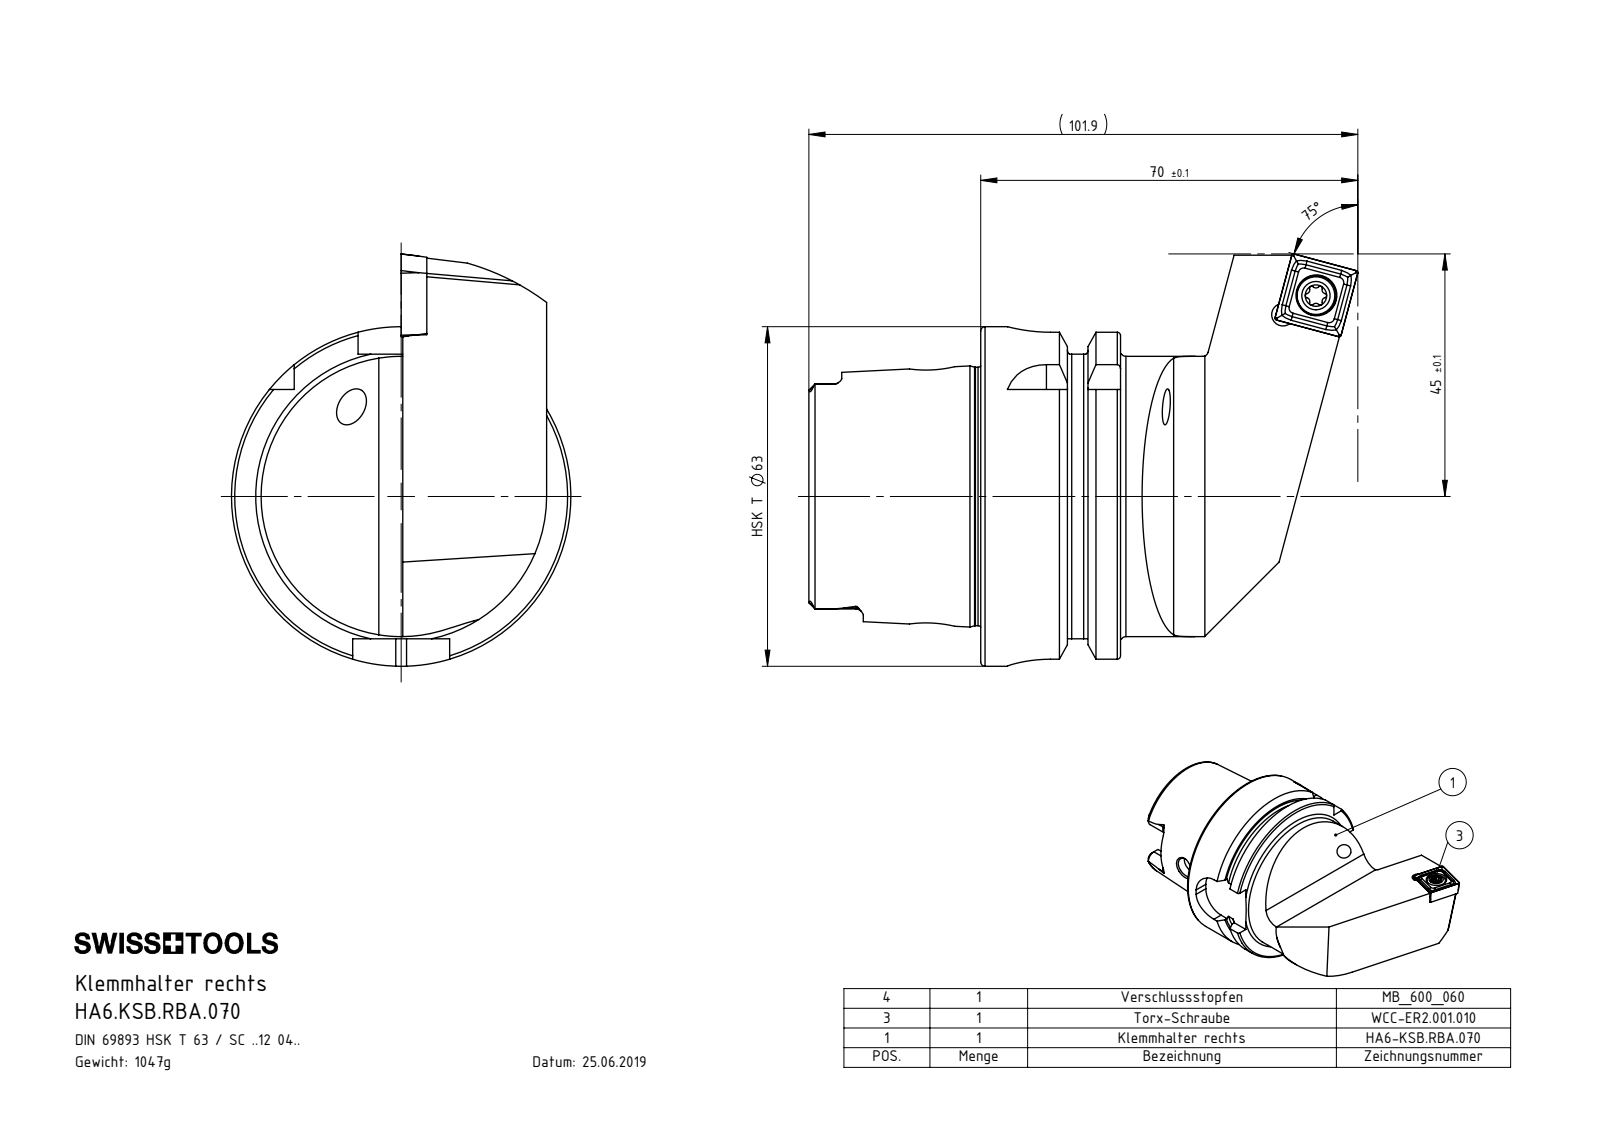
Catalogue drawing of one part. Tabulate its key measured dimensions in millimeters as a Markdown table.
| quantity | value |
| --- | --- |
| part name | HA6.KSB.RBA.070; HA6-KSB.RBA.070_A_Fertigbearbeitung; KVT_MB_600_060; WCC-ER2.001.010_A (+1 more) |
| STEP written by | SolidWorks 2017 (AUTOMOTIVE_DESIGN) |
| units | millimeters |
| bodies | 6 solids, 326 faces (86 planar, 91 cylindrical, 149 other) |
| overall size | 101.9 × 76.5 × 63 |
| volume | 133 417 mm³ |
| surface area | 30 813 mm² |
| round holes (diameter × count) | 4.2 × 2, 5 × 2, 5.5 × 1, 7.5 × 1, 7.6 × 1, 8.4 × 1, 10 × 1, 17 × 1, 19 × 1, 34 × 1, 40 × 1 |
| round bosses / shafts (diameter × count) | 63 × 1, 54.95 × 1, 52 × 1, 47.94 × 1, 7 × 1, 6 × 1, 5 × 1 |
| partial cylindrical surfaces (radius × count) | 0.39 × 6, 1.4 × 6, 2.88 × 4, 8 × 4, 0.69 × 3, 0.69 × 3, 6 × 1, 27 × 1 |
| main face-to-face distances | 26.7, 25.95, 16, 9.95, 31.9, 41.85, 57.85, 22.24, 4.46, 52.8 |
| hole center spacings | 7.07, 7.17, 59.57, 66.61, 66.72 |
